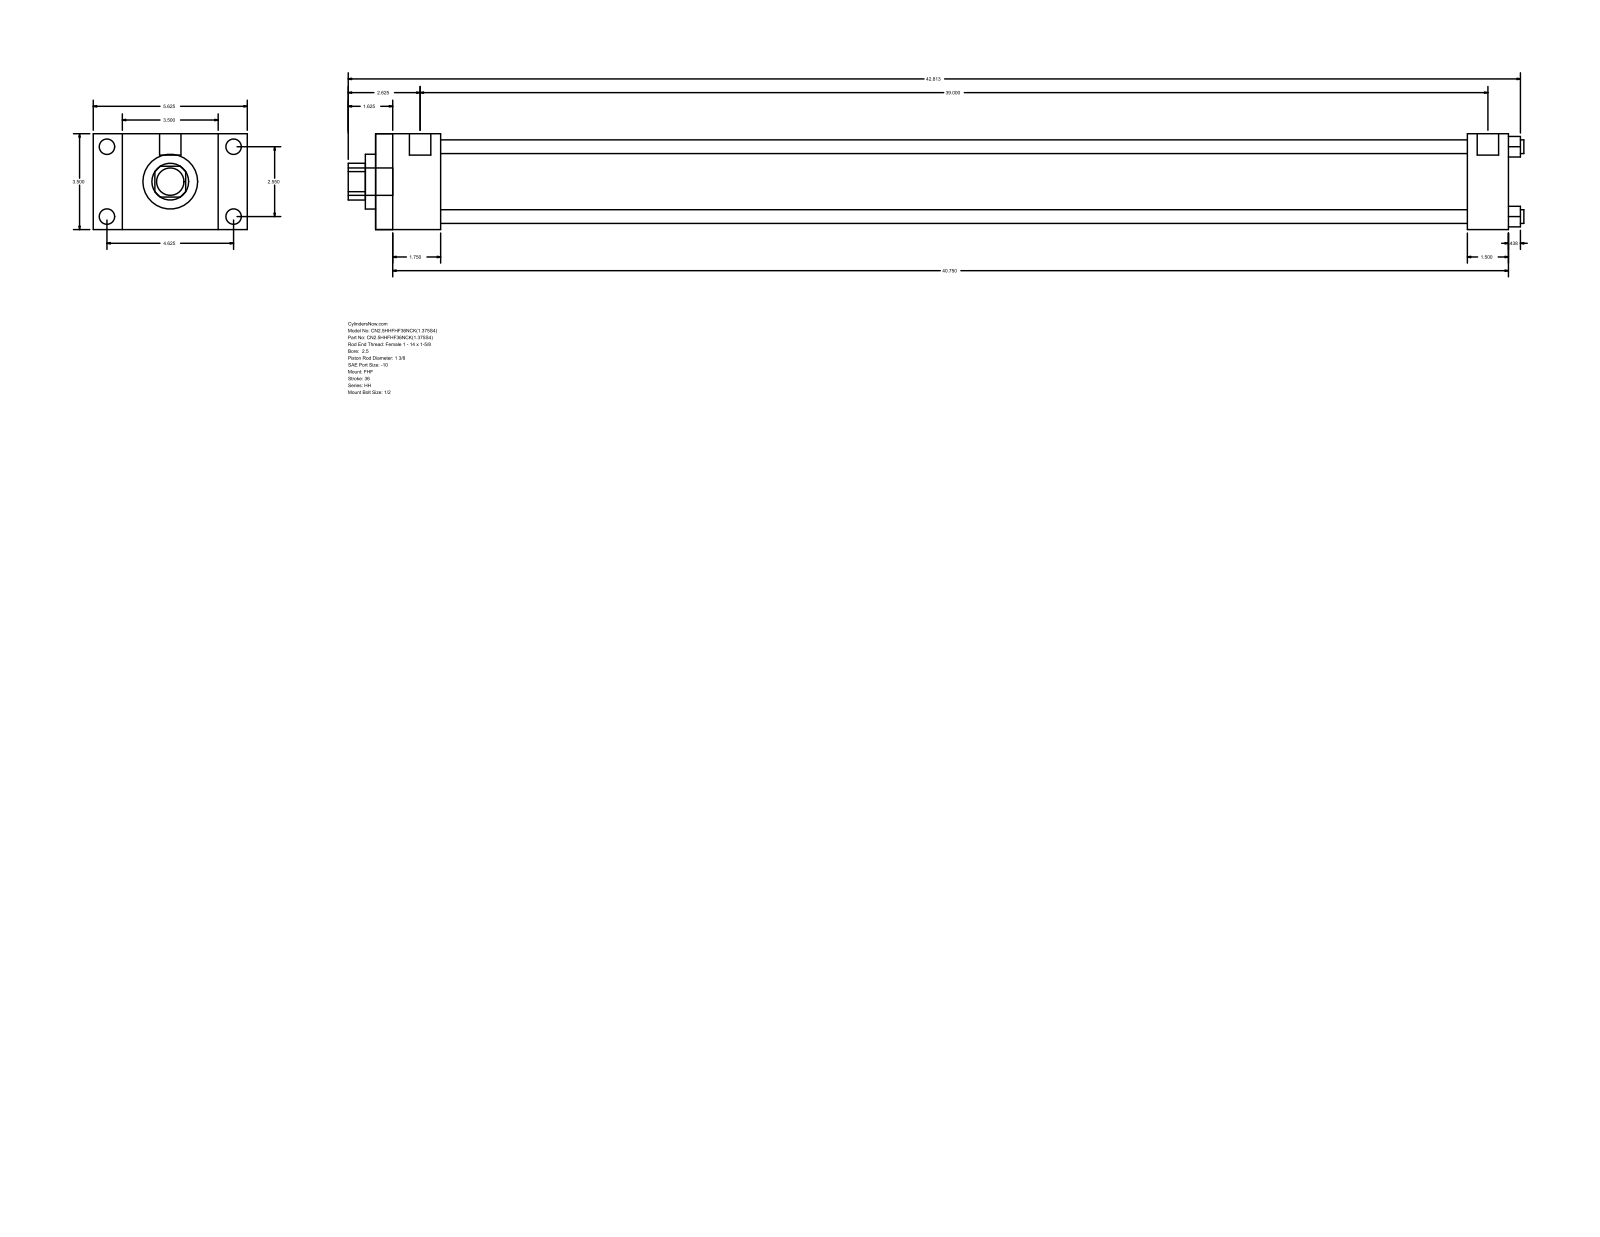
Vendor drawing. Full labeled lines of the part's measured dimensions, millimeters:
Part name (STEP PRODUCT): HH_FHF__0250_1.375
STEP written by: GSSL Pune (CONFIG_CONTROL_DESIGN)
Units: millimetres
Bodies: 0 solids, 88 faces (60 planar, 28 cylindrical, 0 other)
Overall size (bounding box): 1090.61 × 142.88 × 88.9
Round holes (diameter × count): ⌀12.7 ×4, ⌀34.92 ×1, ⌀50.8 ×1, ⌀73.03 ×1
Round bosses / shafts (diameter × count): ⌀14.3 ×4, ⌀5.56 ×4, ⌀19.84 ×2, ⌀25.4 ×1
Partial cylindrical surfaces — rounded edges, fillets, slot ends (radius × count): R17.06 ×1
Main face-to-face distances: 88.9, 60.32, 26.99, 115.89, 1050.93, 990.61, 142.88, 1012.82, 952.5, 38.11
Hole centre spacings: 45.79, 64.76, 91.58
